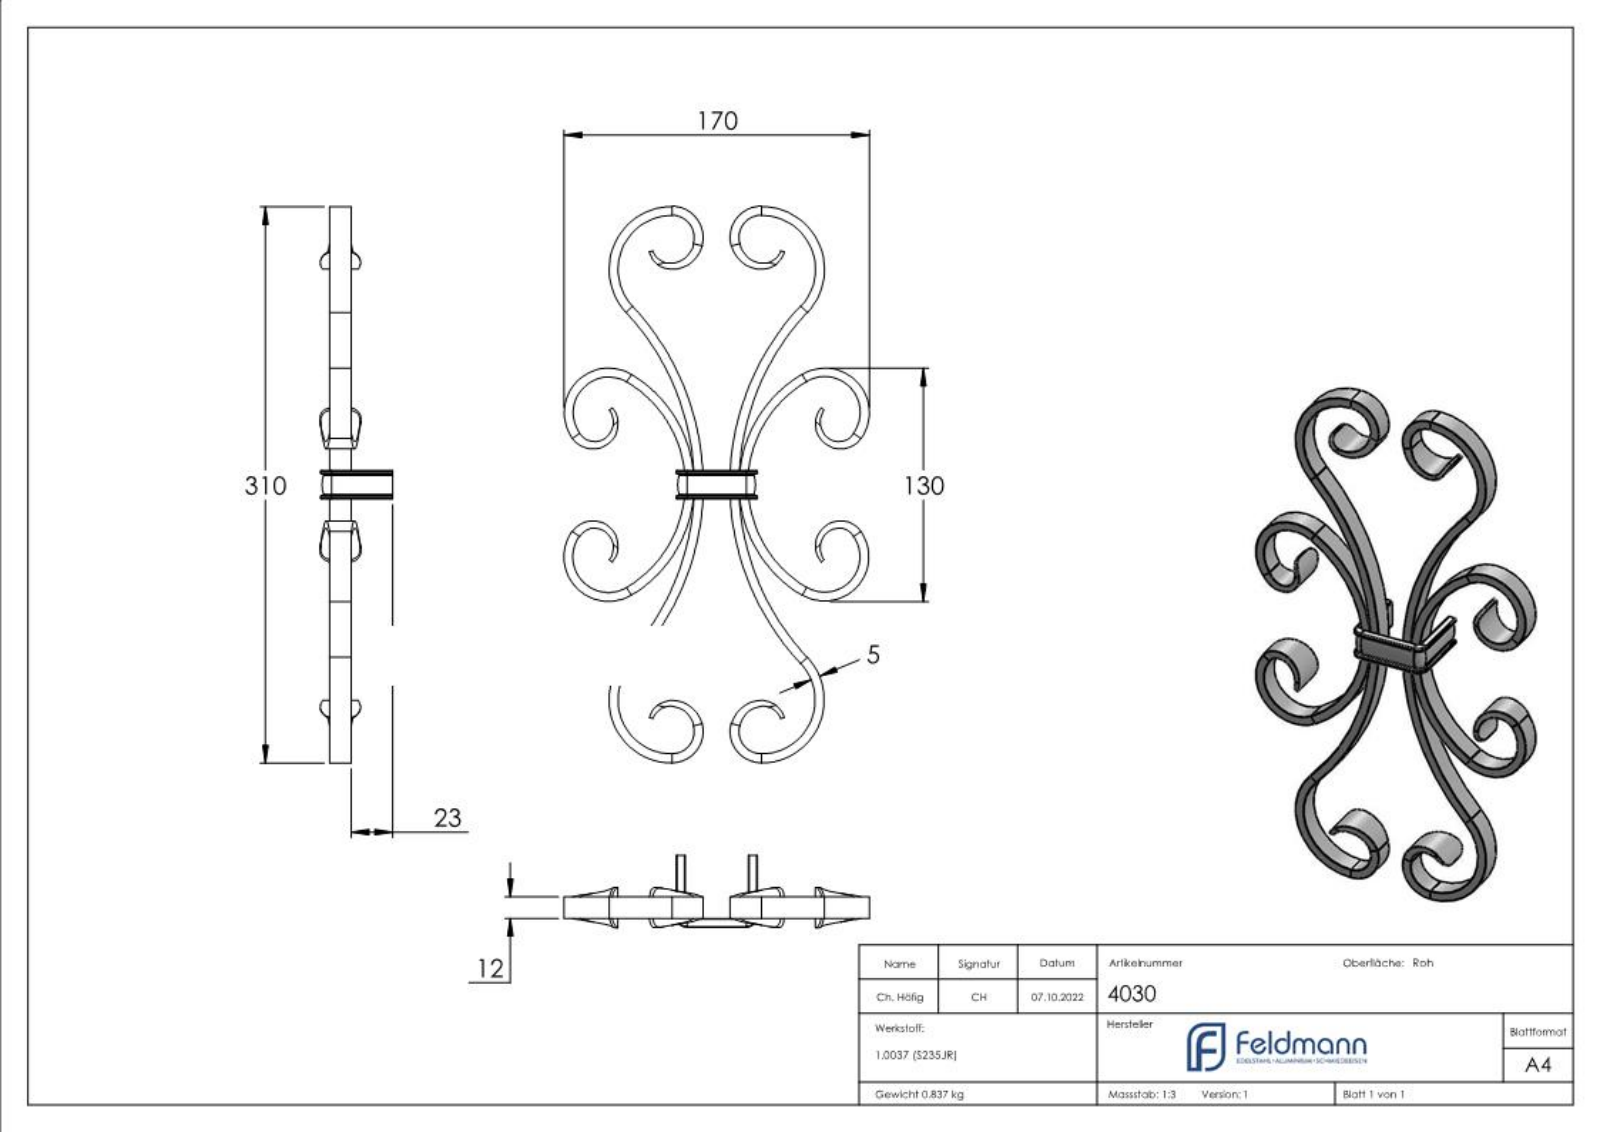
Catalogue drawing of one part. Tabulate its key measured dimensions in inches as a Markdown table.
| quantity | value |
| --- | --- |
| part name | 4030 |
| STEP written by | SolidWorks 2018 (CONFIG_CONTROL_DESIGN) |
| units | inches |
| bodies | 1 solid, 423 faces (188 planar, 65 cylindrical, 170 other) |
| overall size | 12.205 × 6.693 × 1.591 |
| volume | 6.541 in³ |
| surface area | 98.23 in² |
| partial cylindrical surfaces (radius × count) | 0.02 × 24, 0.492 × 4, 0.689 × 4, 0.778 × 4, 0.974 × 4, 1.181 × 4, 1.378 × 4, 0.728 × 3 |
| main face-to-face distances | 0.472, 0.63, 1.386, 0.197, 0.079, 0.551, 1.583, 0.906, 1.378, 1.78 |
